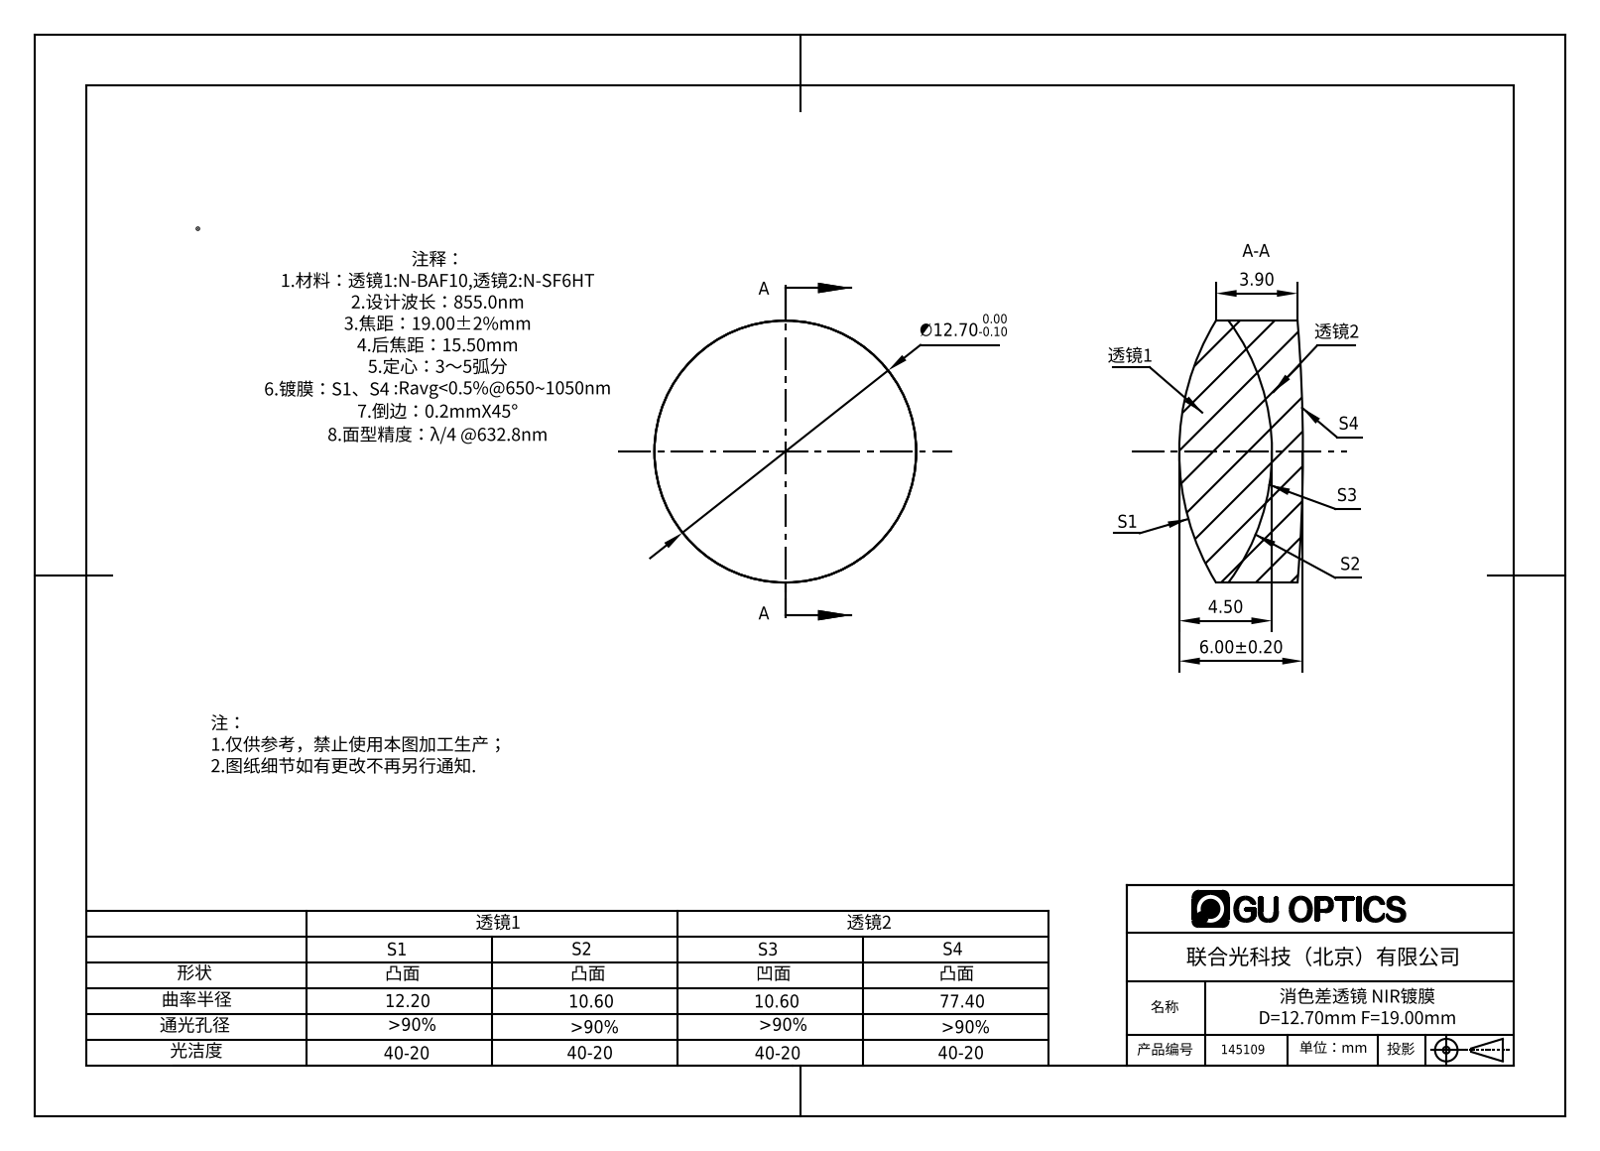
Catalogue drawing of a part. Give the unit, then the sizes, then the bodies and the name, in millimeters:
Units: millimetres
Overall size (bounding box): 12.7 × 12.7 × 6
Round bosses / shafts (diameter × count): ⌀12.7 ×1
Volume: 634 mm³ · Surface area: 703 mm²
Bodies: 2 solids, 12 faces (0 planar, 4 cylindrical, 8 other)
Part name (STEP PRODUCT): 145109
STEP written by: SolidWorks 2016 (AUTOMOTIVE_DESIGN)
